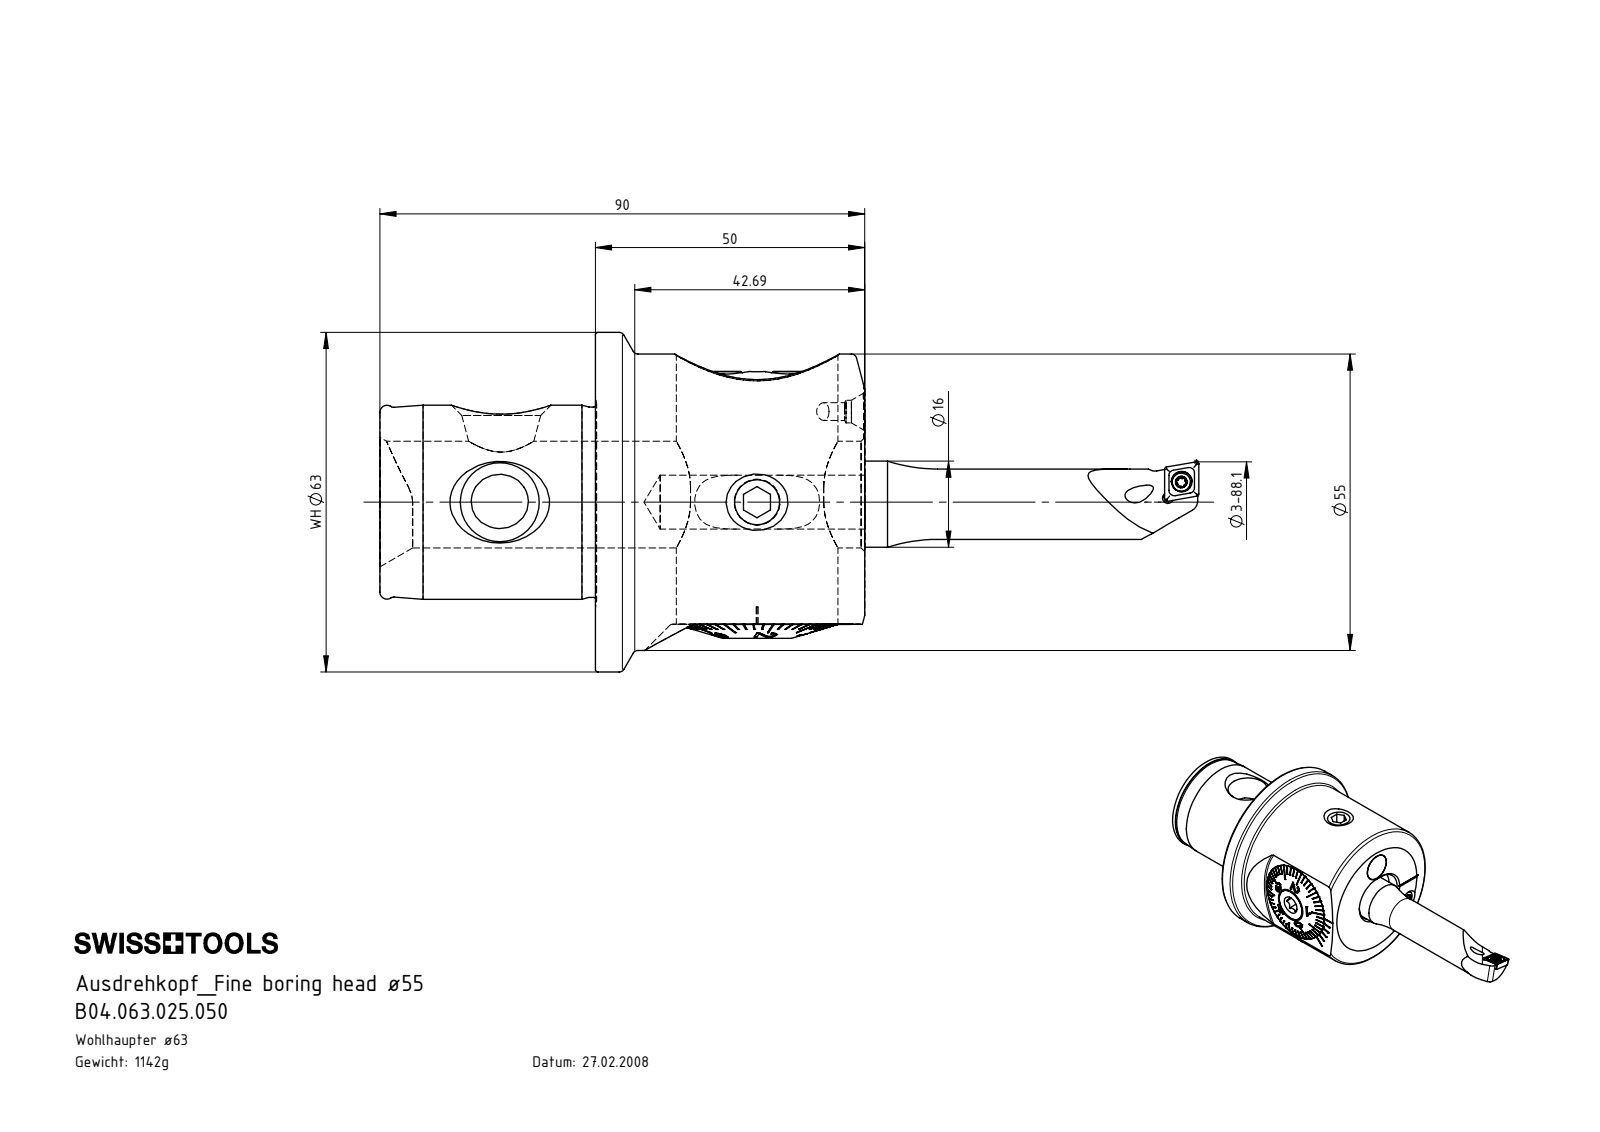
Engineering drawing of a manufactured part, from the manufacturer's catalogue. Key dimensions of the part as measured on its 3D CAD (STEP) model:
Part name (STEP PRODUCT): Klebstoff D10; A55-BG3.011.033_A_gekrzt; A55-BG1.014.041; A55-BG2.015.007_B (+8 more)
STEP written by: SolidWorks 2017 (CONFIG_CONTROL_DESIGN)
Units: millimetres
Bodies: 19 solids, 869 faces (348 planar, 165 cylindrical, 356 other)
Overall size (bounding box): 152 × 63 × 63
Volume: 145 778 mm³ · Surface area: 48 782 mm²
Round holes (diameter × count): ⌀8.5 ×3, ⌀2 ×2, ⌀3 ×2, ⌀1 ×1, ⌀1.6 ×1, ⌀2.05 ×1, ⌀2.8 ×1, ⌀3.3 ×1, ⌀3.85 ×1, ⌀4.2 ×1, ⌀8 ×1, ⌀10 ×1
Round bosses / shafts (diameter × count): ⌀10 ×3, ⌀63 ×1, ⌀55 ×1, ⌀36 ×1, ⌀35.3 ×1, ⌀30 ×1, ⌀29.98 ×1, ⌀29.9 ×1
Partial cylindrical surfaces — rounded edges, fillets, slot ends (radius × count): R0.21 ×6, R0.34 ×6, R0.59 ×6, R0.36 ×5, R3.2 ×3, R8.5 ×2, R0.36 ×1, R0.5 ×1
Main face-to-face distances: 50, 5.3, 2.8, 2.5, 40, 90, 6.48, 3.68, 1.18, 5
Hole centre spacings: 7.25, 14.5, 3.89, 4, 14.7, 19.16, 20.91, 28.48
